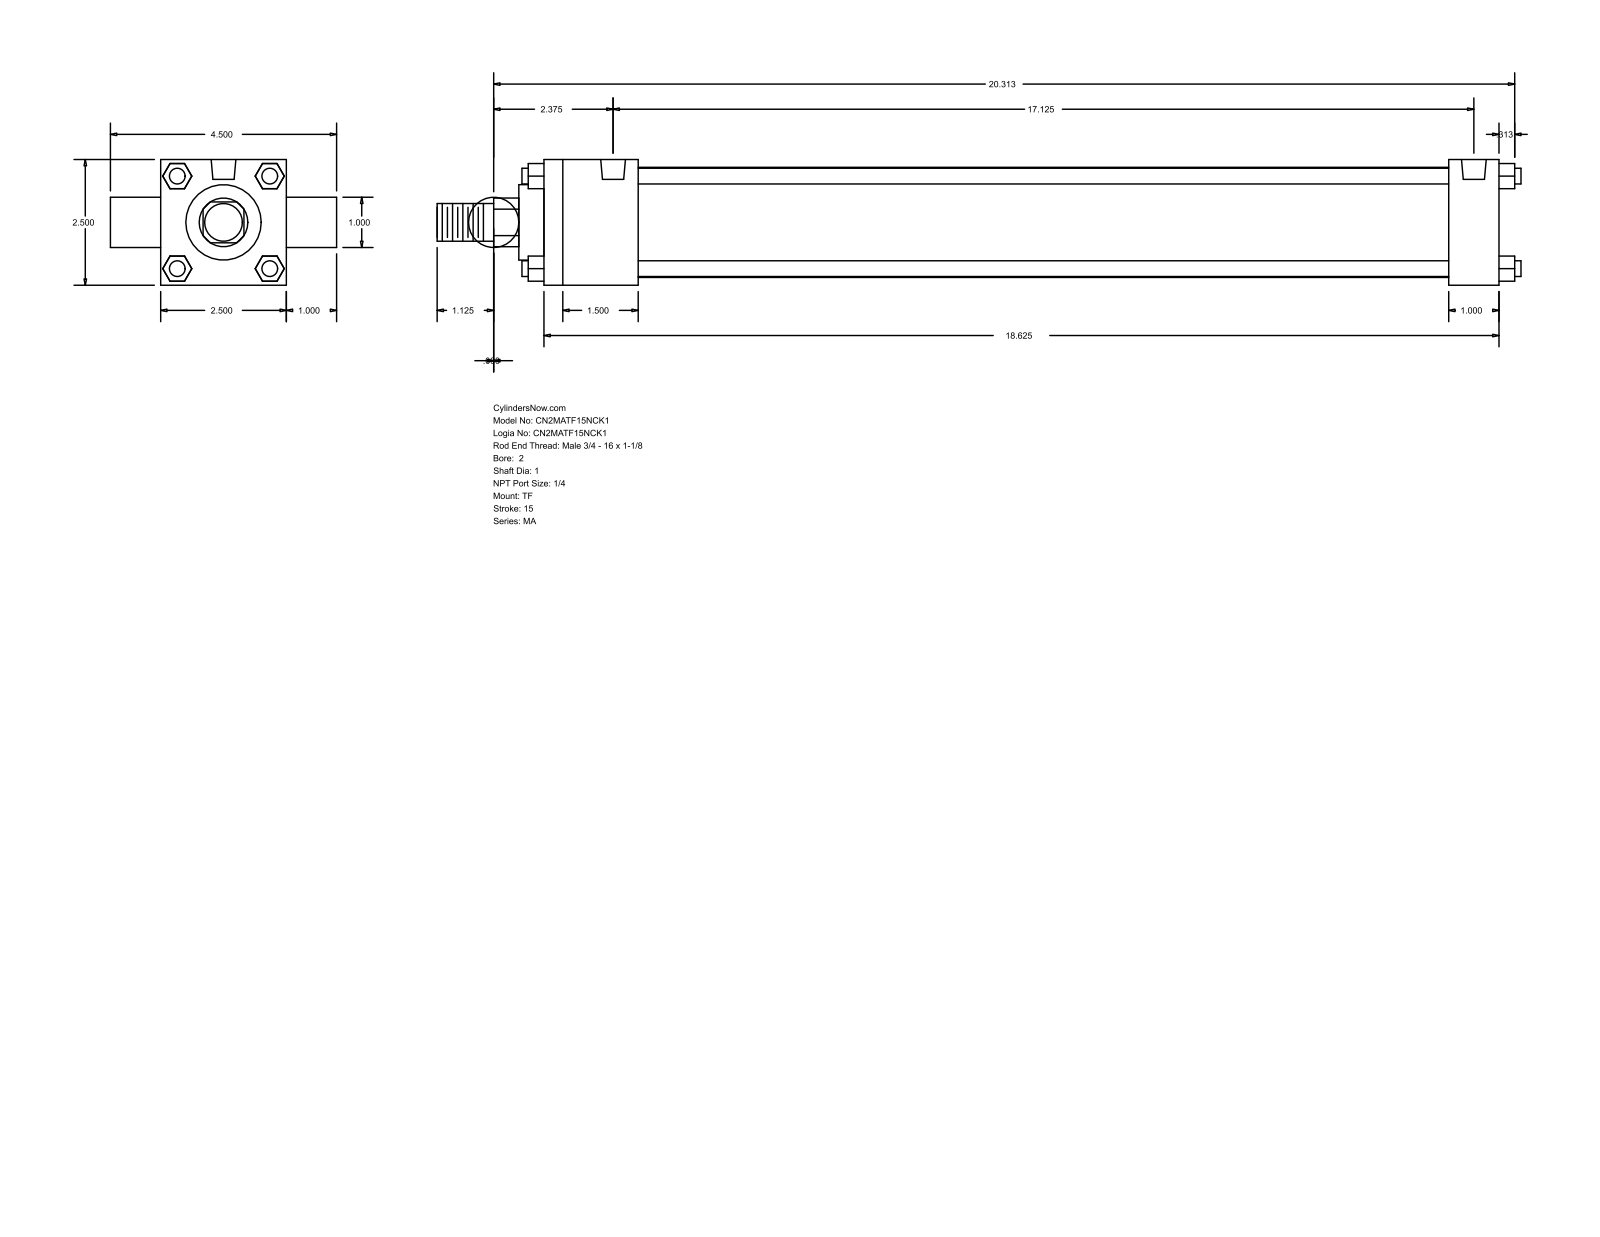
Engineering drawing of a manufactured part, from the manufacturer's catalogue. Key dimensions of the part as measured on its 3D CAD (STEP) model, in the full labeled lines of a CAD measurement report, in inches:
Part name (STEP PRODUCT): MA_TF__0200_1
STEP written by: GSSL Pune (CONFIG_CONTROL_DESIGN)
Units: inches
Bodies: 0 solids, 120 faces (92 planar, 28 cylindrical, 0 other)
Overall size (bounding box): 21.563 × 4.5 × 2.5
Round holes (diameter × count): ⌀0.313 ×3, ⌀0.492 ×2
Round bosses / shafts (diameter × count): ⌀0.313 ×4, ⌀1 ×2, ⌀2.19 ×1, ⌀1.5 ×1, ⌀0.75 ×1
Partial cylindrical surfaces — rounded edges, fillets, slot ends (radius × count): R0.484 ×1
Main face-to-face distances: 2.5, 1, 19, 0.5, 1.875, 18, 16.125, 17.125, 3.5, 0.92
Hole centre spacings: 17.125
